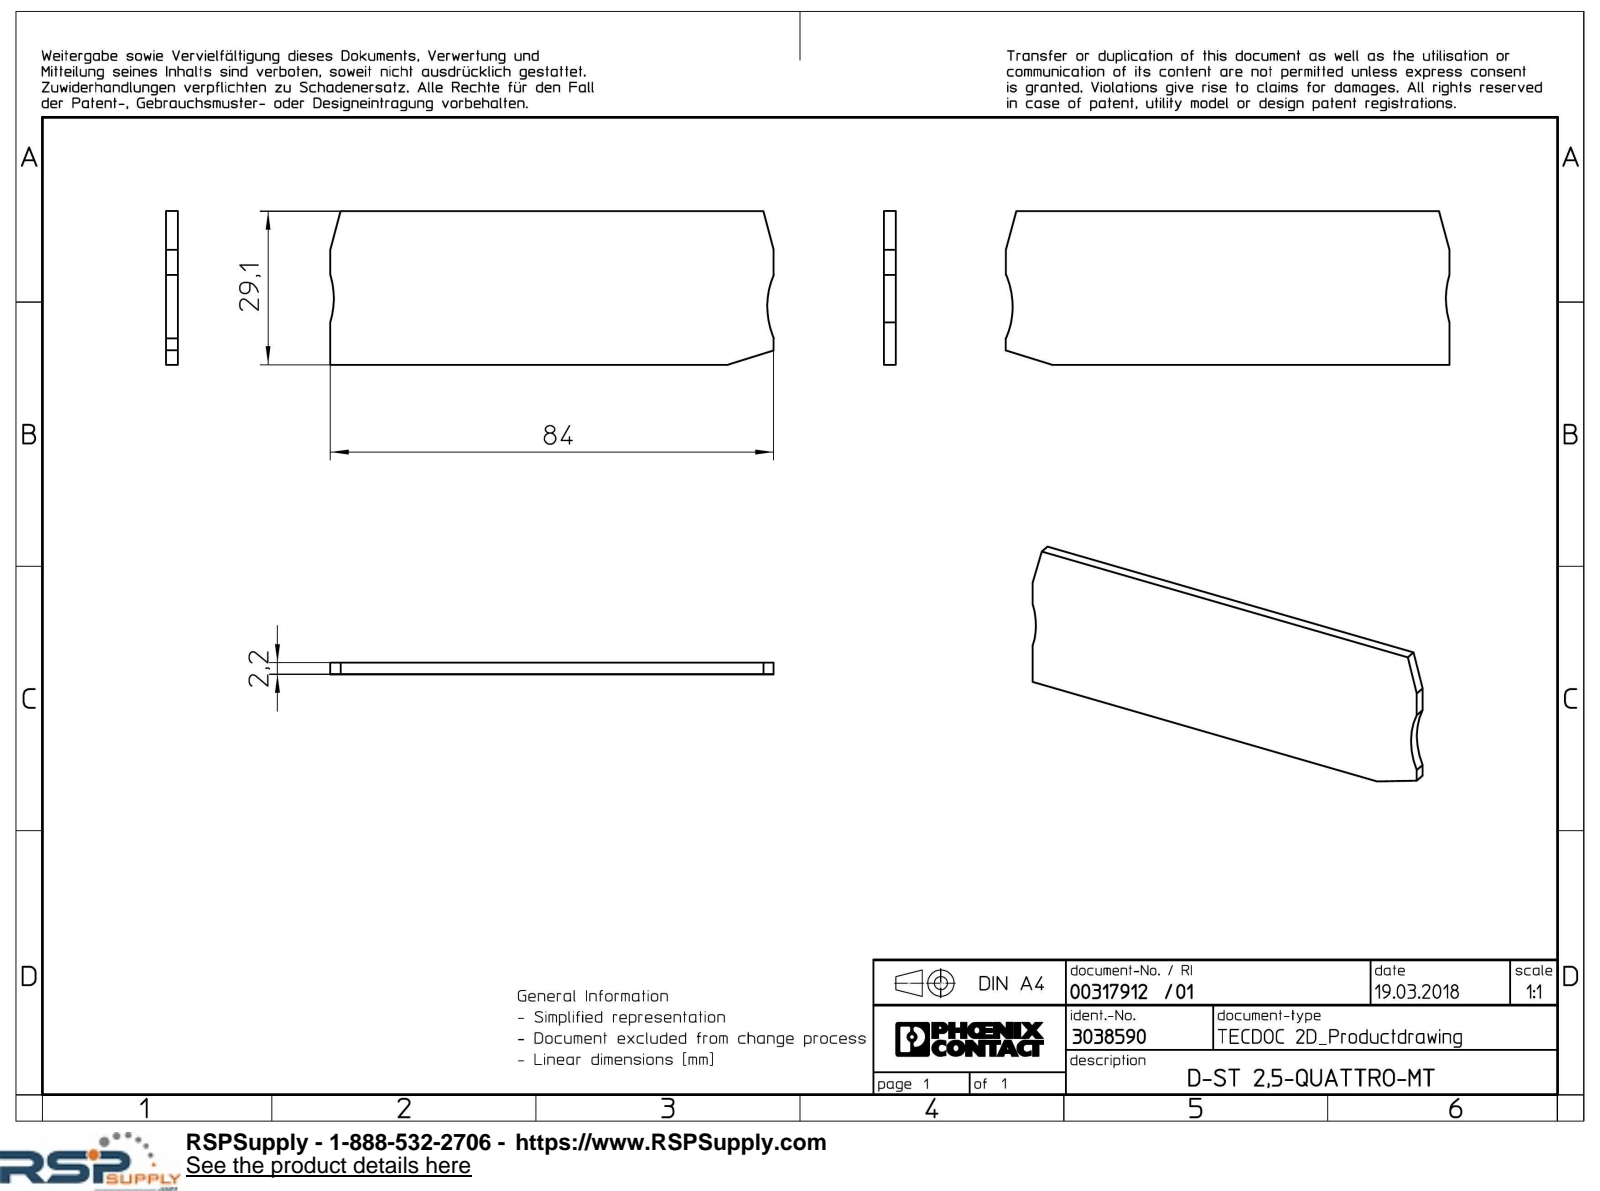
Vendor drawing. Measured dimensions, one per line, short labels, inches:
name: D_ST_25-QUATTRO-MT-SELECT
written by: Creo Elements/Direct Modeling 20.1A 29-Sep-2018 (C) Parametric Technology GmbH (AUTOMOTIVE_DESIGN)
unit: in
bodies: 1 solid, 13 faces (11 planar, 2 cylindrical, 0 other)
size: 3.307 × 1.144 × 0.087
volume: 0.322 in³; area: 8.193 in²
rounds: 2× R0.591
face distances: 0.087, 1.144, 3.307
